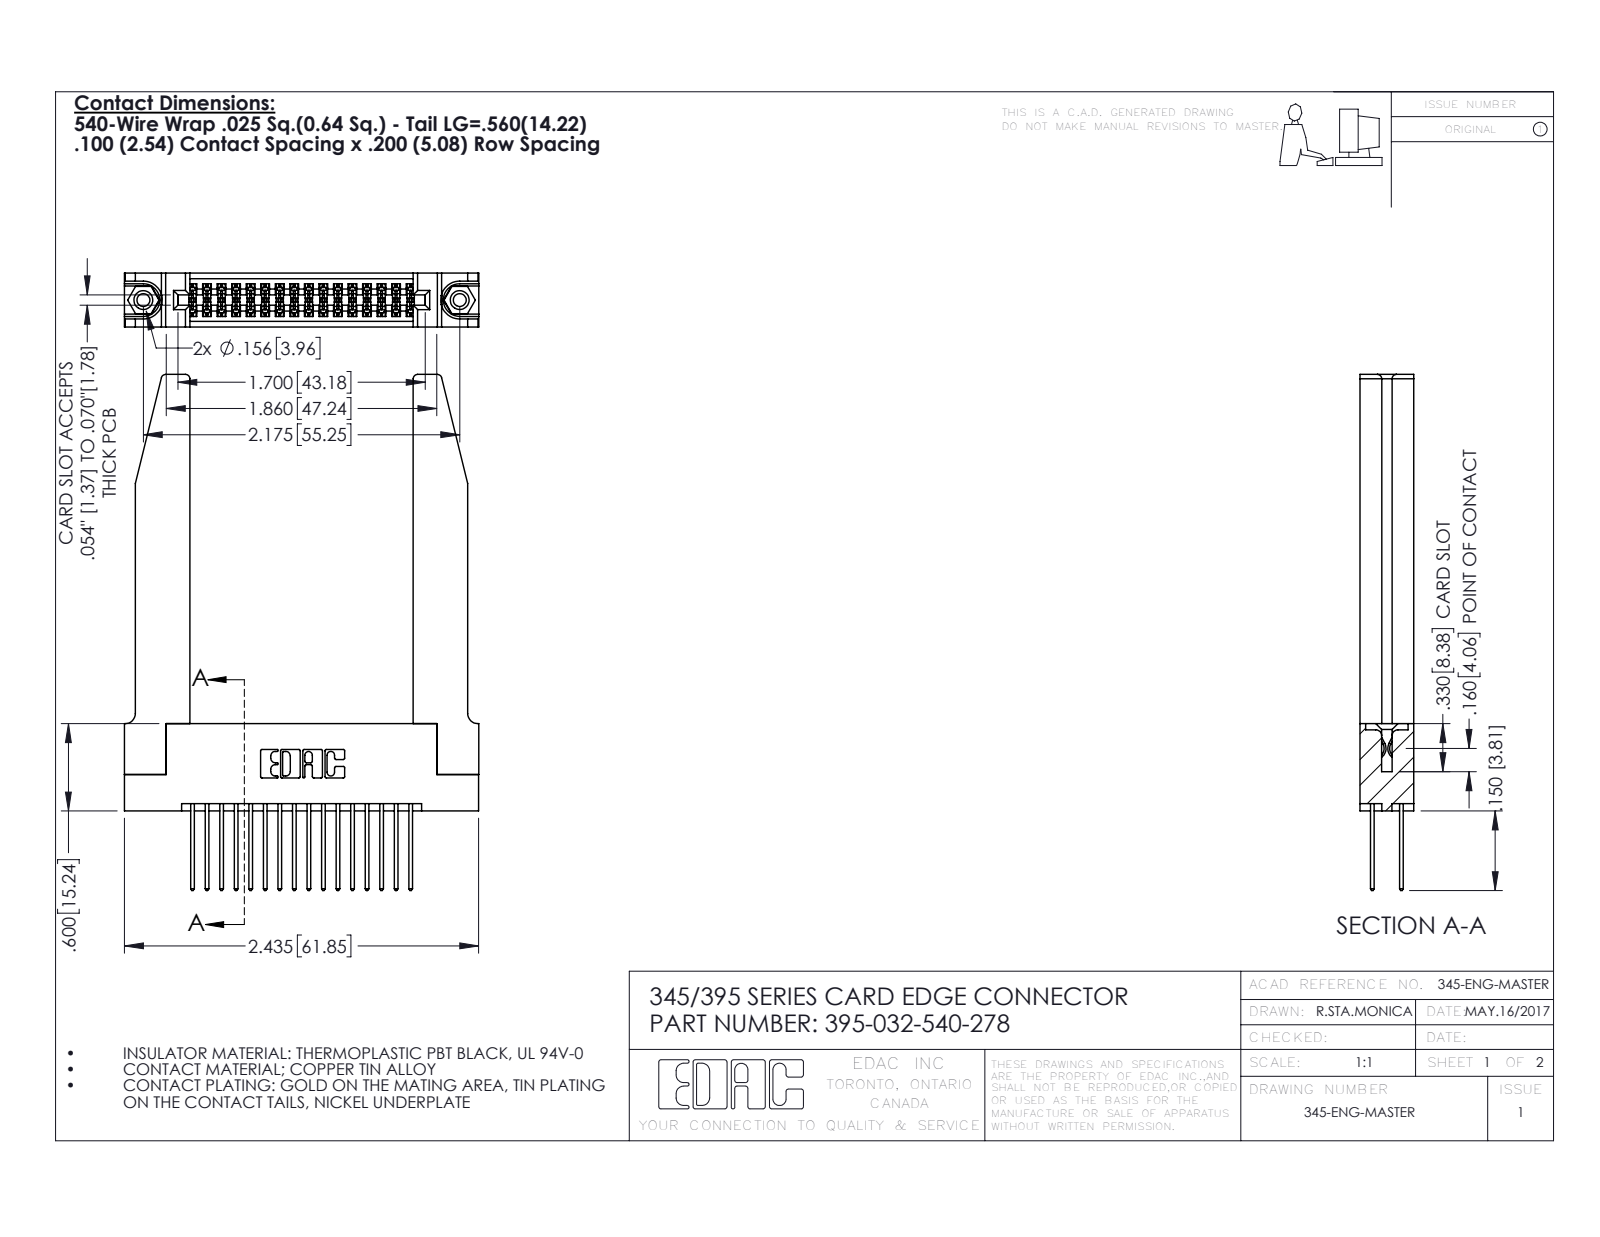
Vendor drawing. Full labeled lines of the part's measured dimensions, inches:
Part name (STEP PRODUCT): 345 Part_Flush Mounting Lugs - 0.156 Dia-TH; 395-032-540-278; 345-292-001_345-293-140; 345-250-001_345-250-001-102 (+1 more)
STEP written by: SolidWorks 2016 (CONFIG_CONTROL_DESIGN)
Units: inches
Bodies: 37 solids, 1960 faces (1278 planar, 630 cylindrical, 52 other)
Overall size (bounding box): 3.547 × 2.436 × 0.37
Volume: 0.834 in³ · Surface area: 24.19 in²
Round holes (diameter × count): ⌀0.089 ×2, ⌀0.125 ×2, ⌀0.156 ×2, ⌀0.064 ×1
Round bosses / shafts (diameter × count): ⌀0.155 ×2
Partial cylindrical surfaces — rounded edges, fillets, slot ends (radius × count): R0.006 ×48, R0.01 ×32, R0.01 ×22, R0.03 ×8, R0.007 ×6, R0.031 ×6, R0.026 ×3, R0.014 ×2
Main face-to-face distances: 0.37, 0.072, 0.298, 0.2, 0.098, 0.272, 0.025, 0.225, 0.148, 0.15
Hole centre spacings: 0.27, 1.942, 2.175
